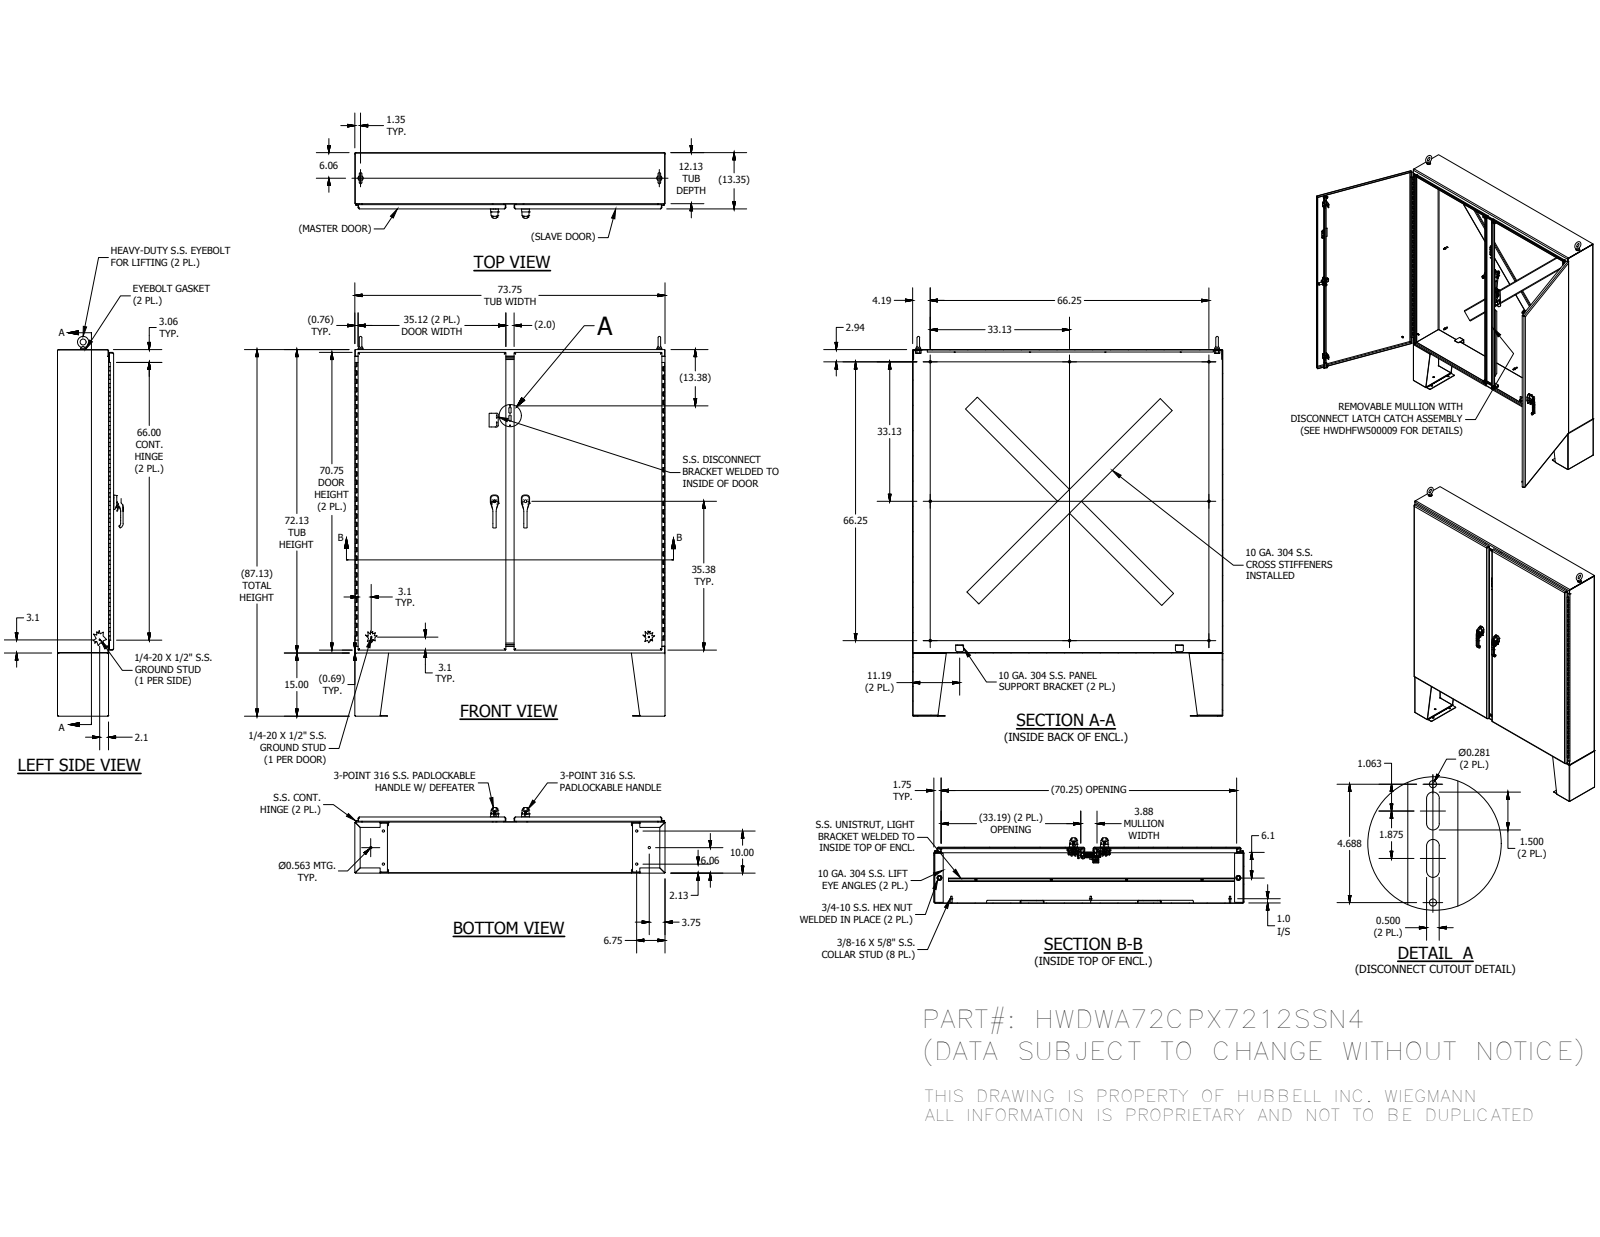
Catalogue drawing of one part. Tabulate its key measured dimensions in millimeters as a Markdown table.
| quantity | value |
| --- | --- |
| part name | WA72CPX7212SSN4BLR; WACPX7212SSN4TOP; WACPX7212SSN4BTM; HFW303115 (+8 more) |
| STEP written by | Autodesk Inventor 2016 (AUTOMOTIVE_DESIGN) |
| units | millimeters |
| bodies | 215 solids, 8964 faces (4203 planar, 3005 cylindrical, 1756 other) |
| overall size | 2292.29 × 1873.25 × 396.15 |
| volume | 31 440 000 mm³ |
| surface area | 23 880 000 mm² |
| round holes (diameter × count) | 6.35 × 20, 9.52 × 18, 14.29 × 18, 4.98 × 12, 7.14 × 10, 4.76 × 9, 6.65 × 8, 3.96 × 6, 4.83 × 6, 5.4 × 6, 7.33 × 6, 7.37 × 6 |
| round bosses / shafts (diameter × count) | 8.38 × 16, 6.35 × 16, 15.88 × 14, 14.29 × 9, 9.52 × 9, 8.56 × 9, 25.4 × 6, 12.7 × 6 |
| partial cylindrical surfaces (radius × count) | 0.5 × 358, 0.3 × 222, 0.51 × 144, 3.17 × 58, 0.47 × 42, 1.27 × 28, 2 × 28, 3.57 × 24 |
| main face-to-face distances | 2.64, 336.39, 333.75, 339.03, 1829.34, 1870.6, 305.33, 31.06, 2.65, 3.17 |
| hole center spacings | 9.65, 19.31, 22.5, 30.36, 31.38, 37.06, 88.97, 98.31 |
